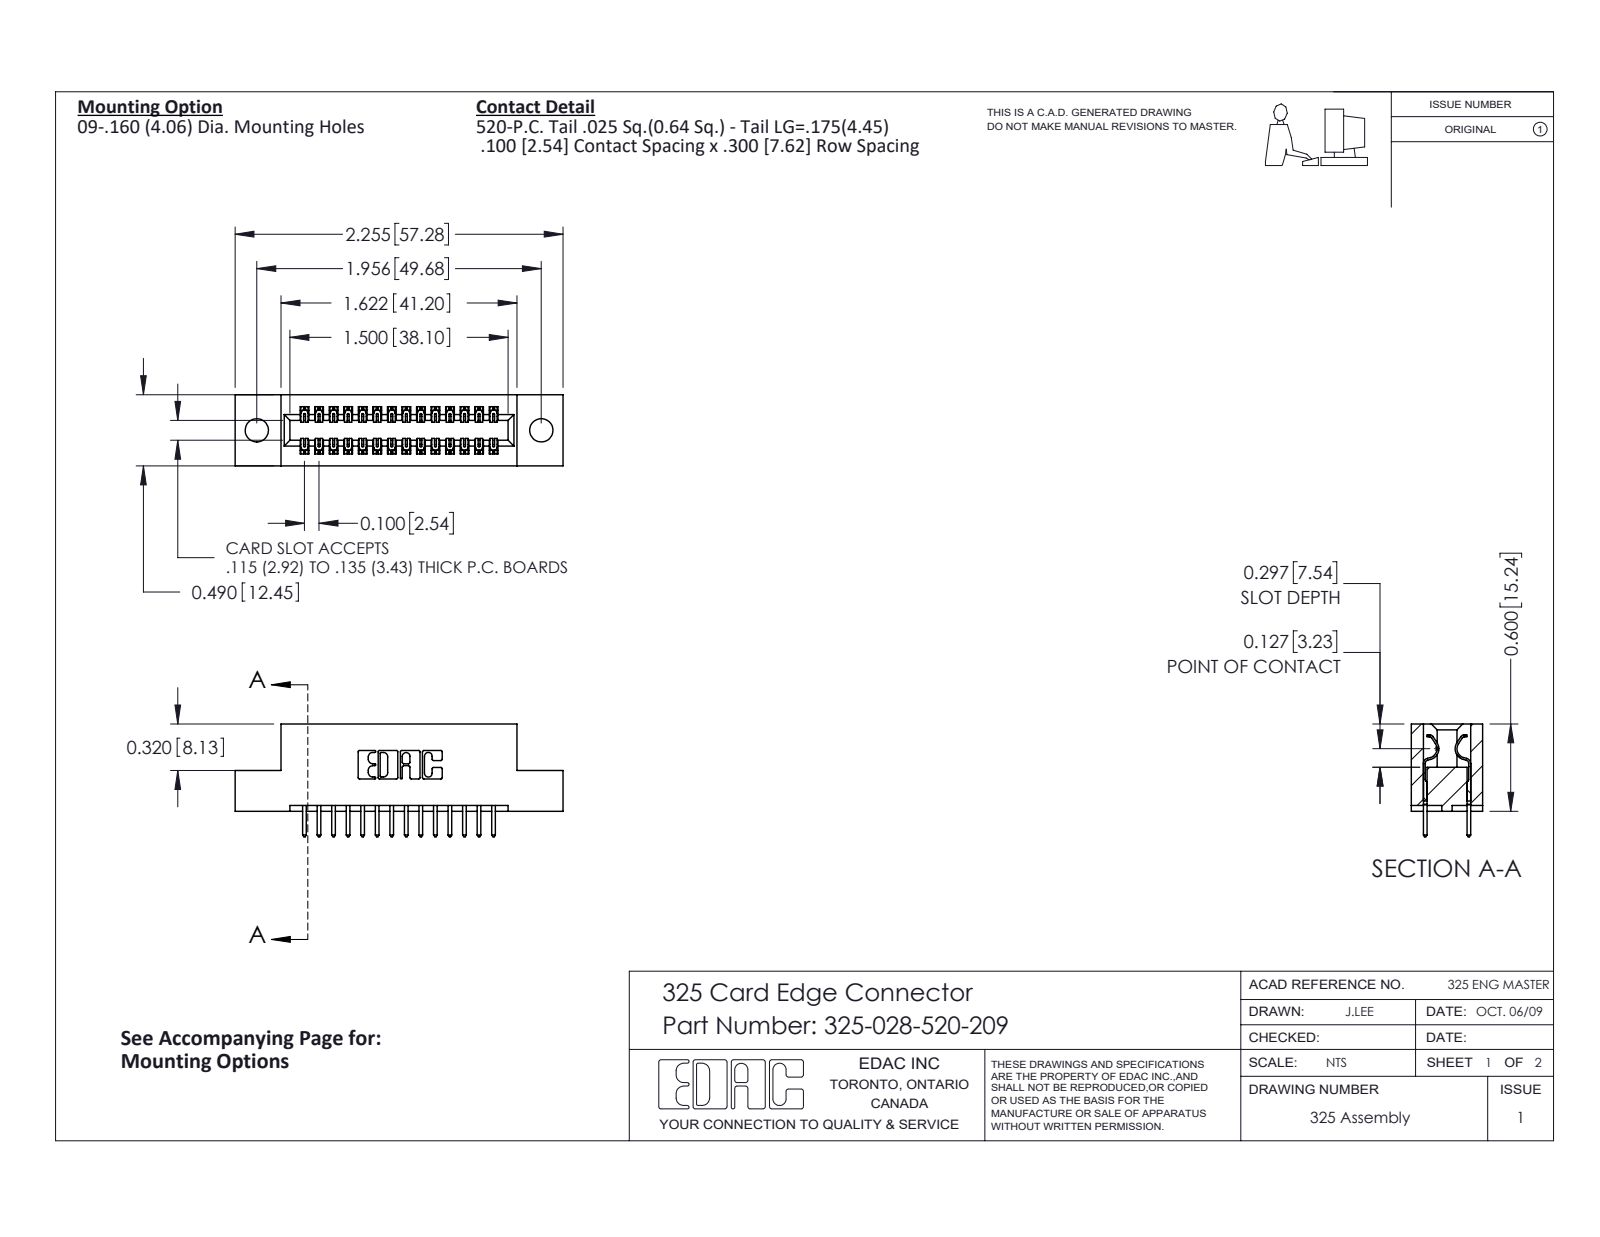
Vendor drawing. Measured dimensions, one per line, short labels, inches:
name: 325-292-001_325-293-120; 325 Part_.160 TH; 325-028-520-209
written by: SolidWorks 2016 (CONFIG_CONTROL_DESIGN)
unit: in
bodies: 29 solids, 1570 faces (1078 planar, 492 cylindrical, 0 other)
size: 2.255 × 0.775 × 0.49
volume: 0.422 in³; area: 11.72 in²
holes: 2× ⌀0.16
rounds: 42× R0.006, 28× R0.01, 22× R0.01, 6× R0.007, 6× R0.031, 3× R0.026, 2× R0.014, 2× R0.022
face distances: 0.083, 0.407, 0.3, 0.49, 0.107, 0.383, 0.025, 0.04, 0.325, 0.1
hole spacings: 1.956
